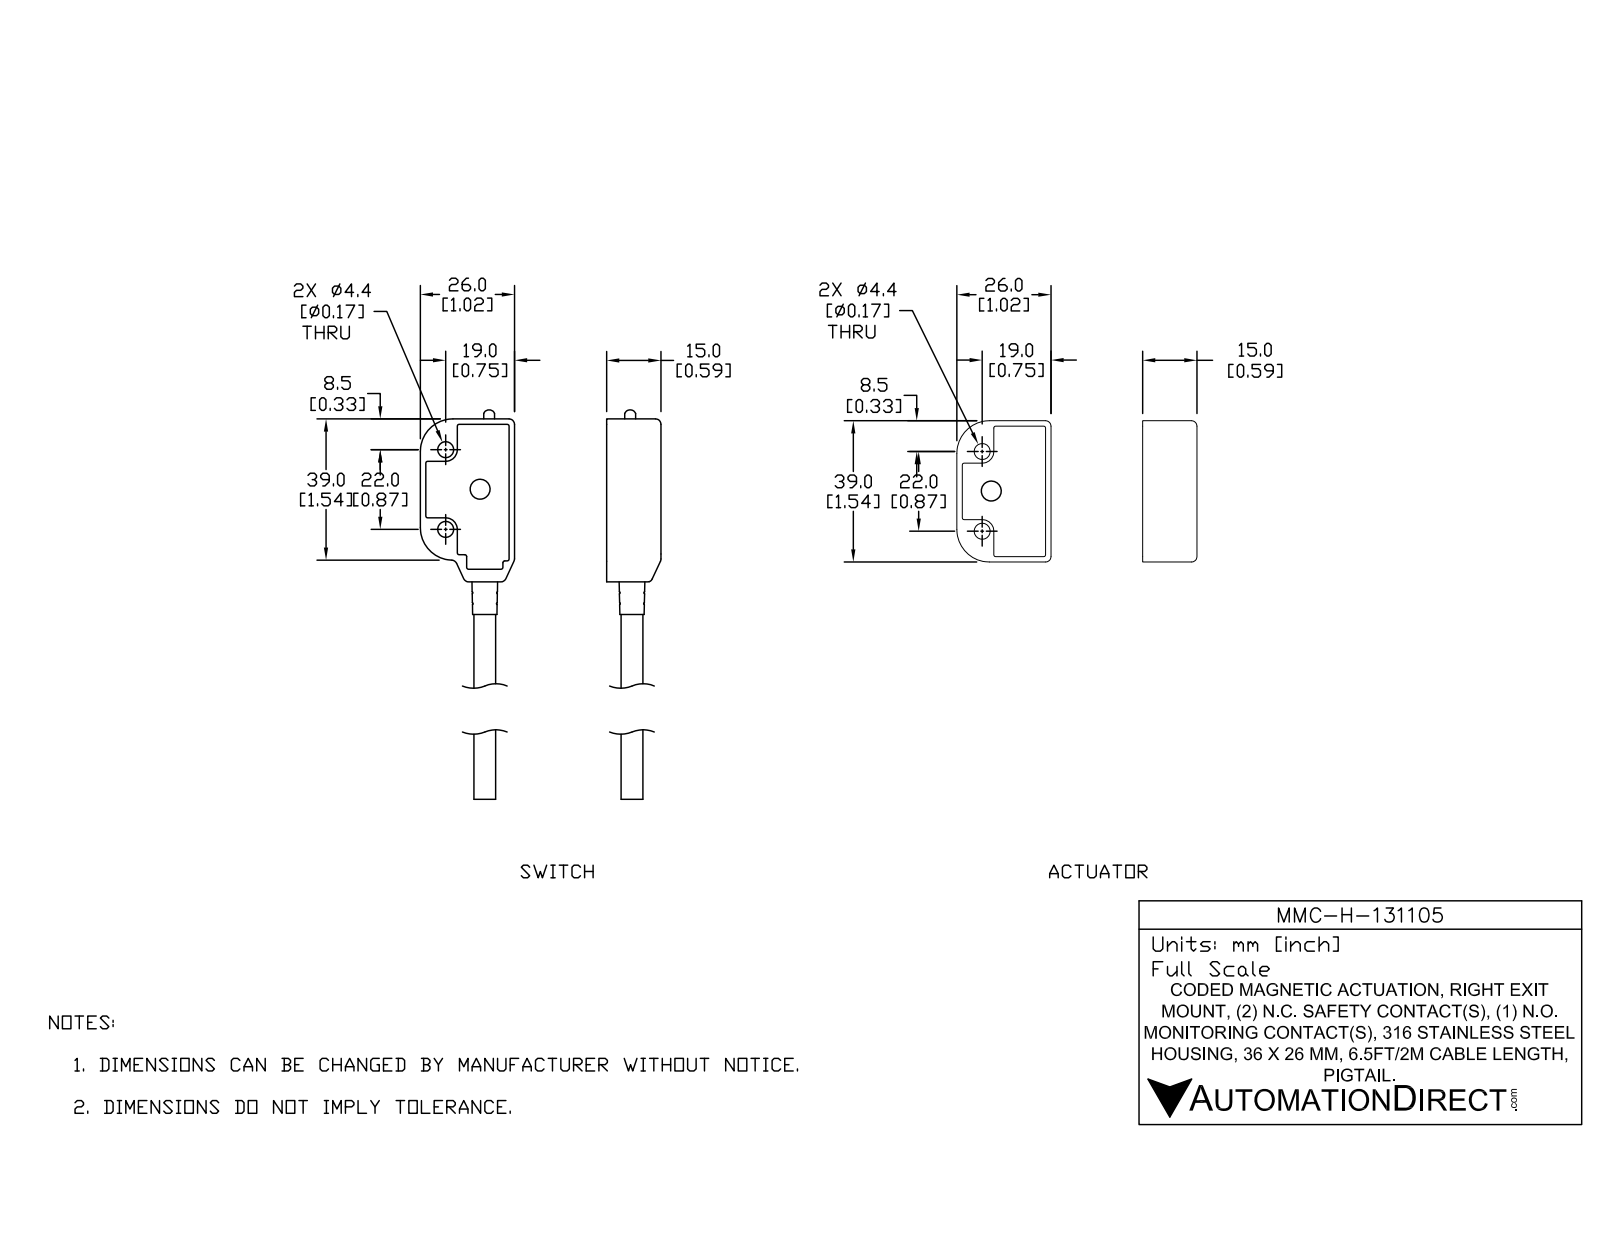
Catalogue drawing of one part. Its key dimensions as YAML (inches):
part_name: "MMC-H-131105; MMC-H-131105_2; MMC-H-131105_1"
step_written_by: "SolidWorks 2017 (AUTOMOTIVE_DESIGN)"
units: inches
bodies: {solids: 9, faces: 599, planar: 178, cylindrical: 232, other: 189}
overall_size: [7.902, 2.087, 0.591]
volume: 1.233
surface_area: 31
round_holes:
  - {diameter: 0.173, count: 4}
  - {diameter: 0.197, count: 2}
  - {diameter: 0.118, count: 1}
  - {diameter: 0.232, count: 1}
  - {diameter: 0.283, count: 1}
round_bosses_or_shafts:
  - {diameter: 0.079, count: 2}
  - {diameter: 0.031, count: 2}
  - {diameter: 0.339, count: 1}
  - {diameter: 0.299, count: 1}
  - {diameter: 0.28, count: 1}
  - {diameter: 0.236, count: 1}
  - {diameter: 0.157, count: 1}
partial_cylinders:
  - {radius: 0.02, count: 82}
  - {radius: 0.012, count: 26}
  - {radius: 0.059, count: 15}
  - {radius: 0.008, count: 8}
  - {radius: 0.157, count: 6}
  - {radius: 0.126, count: 4}
  - {radius: 0.13, count: 4}
  - {radius: 0.181, count: 4}
face_to_face_distances: [0.059, 0.575, 0.516, 0.098, 0.461, 0.52, 0.055, 0.591, 0.531, 0.965]
hole_center_spacings: [0.866, 1.535, 1.763, 0.076, 0.44, 0.448, 0.569, 0.575]
